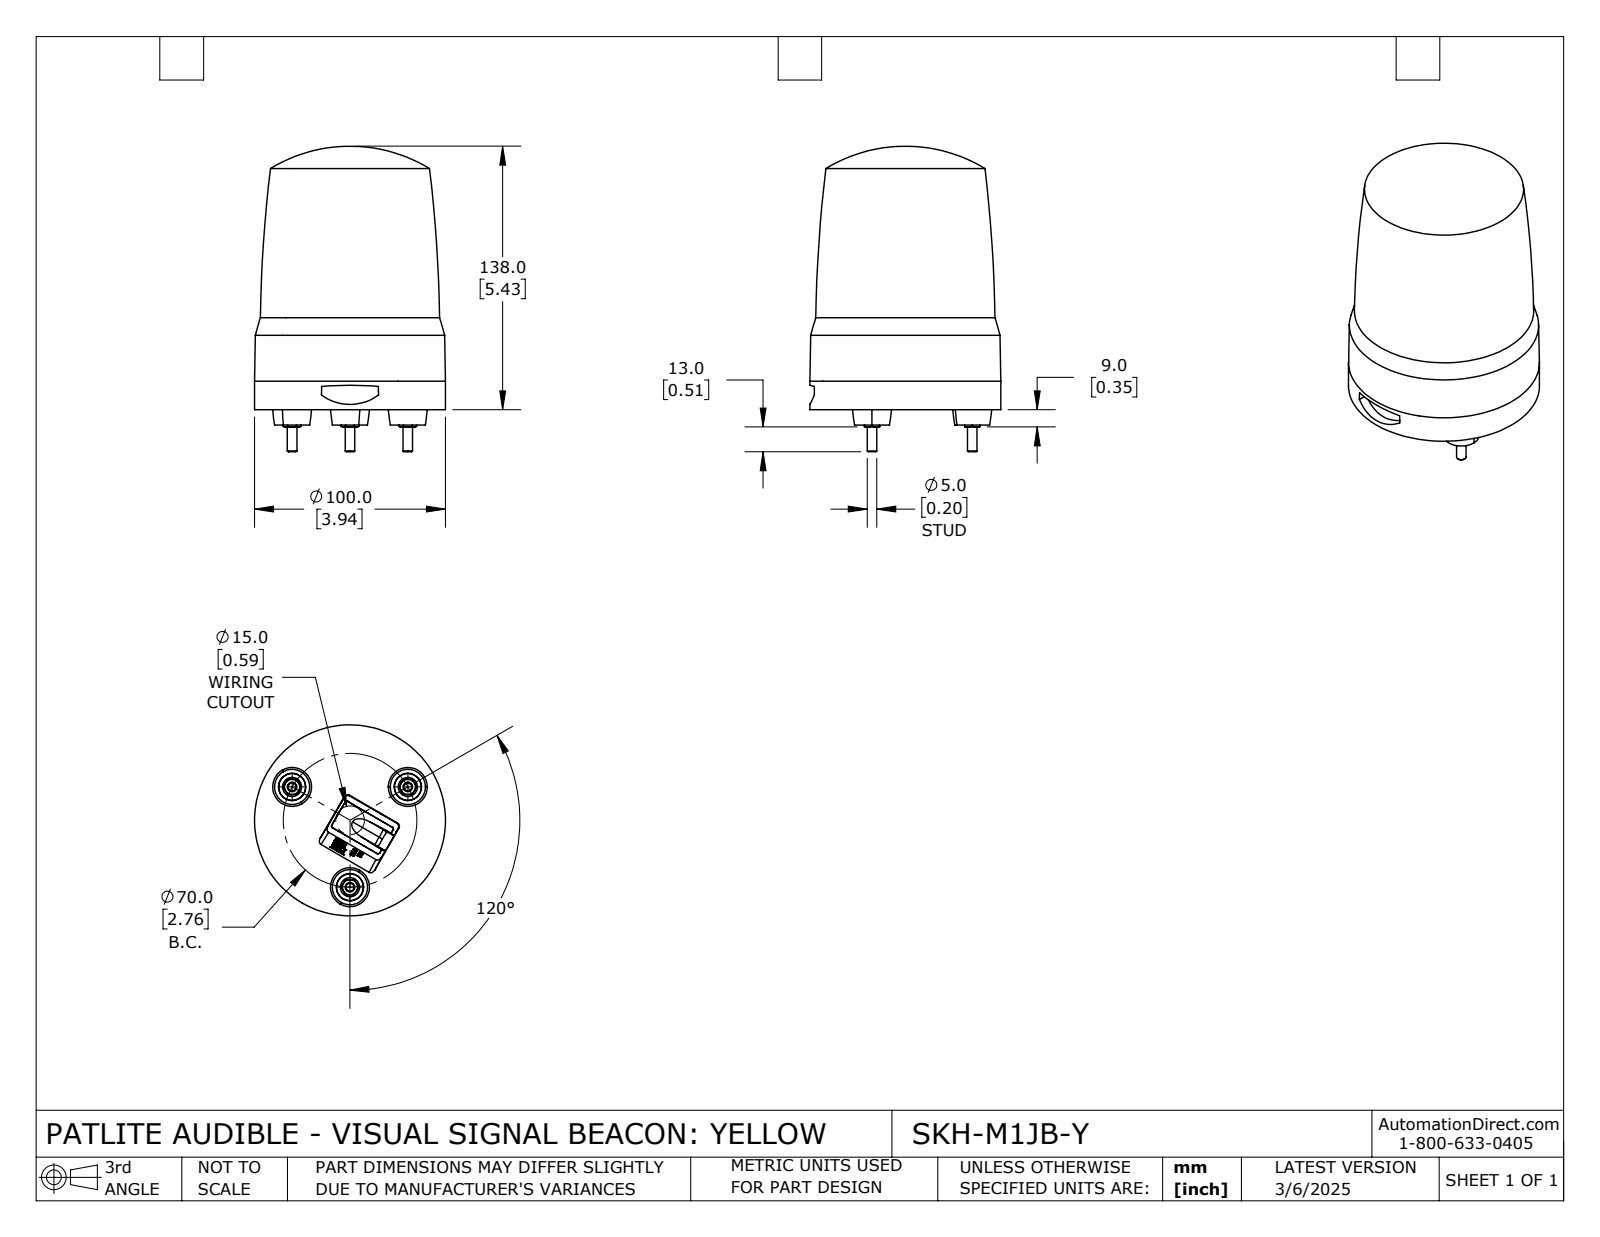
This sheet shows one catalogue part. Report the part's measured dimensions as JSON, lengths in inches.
{"part_name": "SKH-M1JB-Y", "step_written_by": "SolidWorks 2024 (CONFIG_CONTROL_DESIGN)", "units": "inches", "bodies": {"solids": 1, "faces": 446, "planar": 211, "cylindrical": 22, "other": 213}, "overall_size": [6.299, 3.937, 3.937], "volume_in3": 54.94, "surface_area_in2": 85.92, "round_bosses_or_shafts": [[0.394, 3], [0.197, 3], [3.937, 1]], "partial_cylinders_radius": [[0.079, 4], [0.199, 2], [1.772, 1], [3.154, 1]], "face_to_face_distances": [0.315, 0.585, 0.27, 0.063, 0.648, 0.333, 0.15, 0.165, 0.435, 0.498]}
